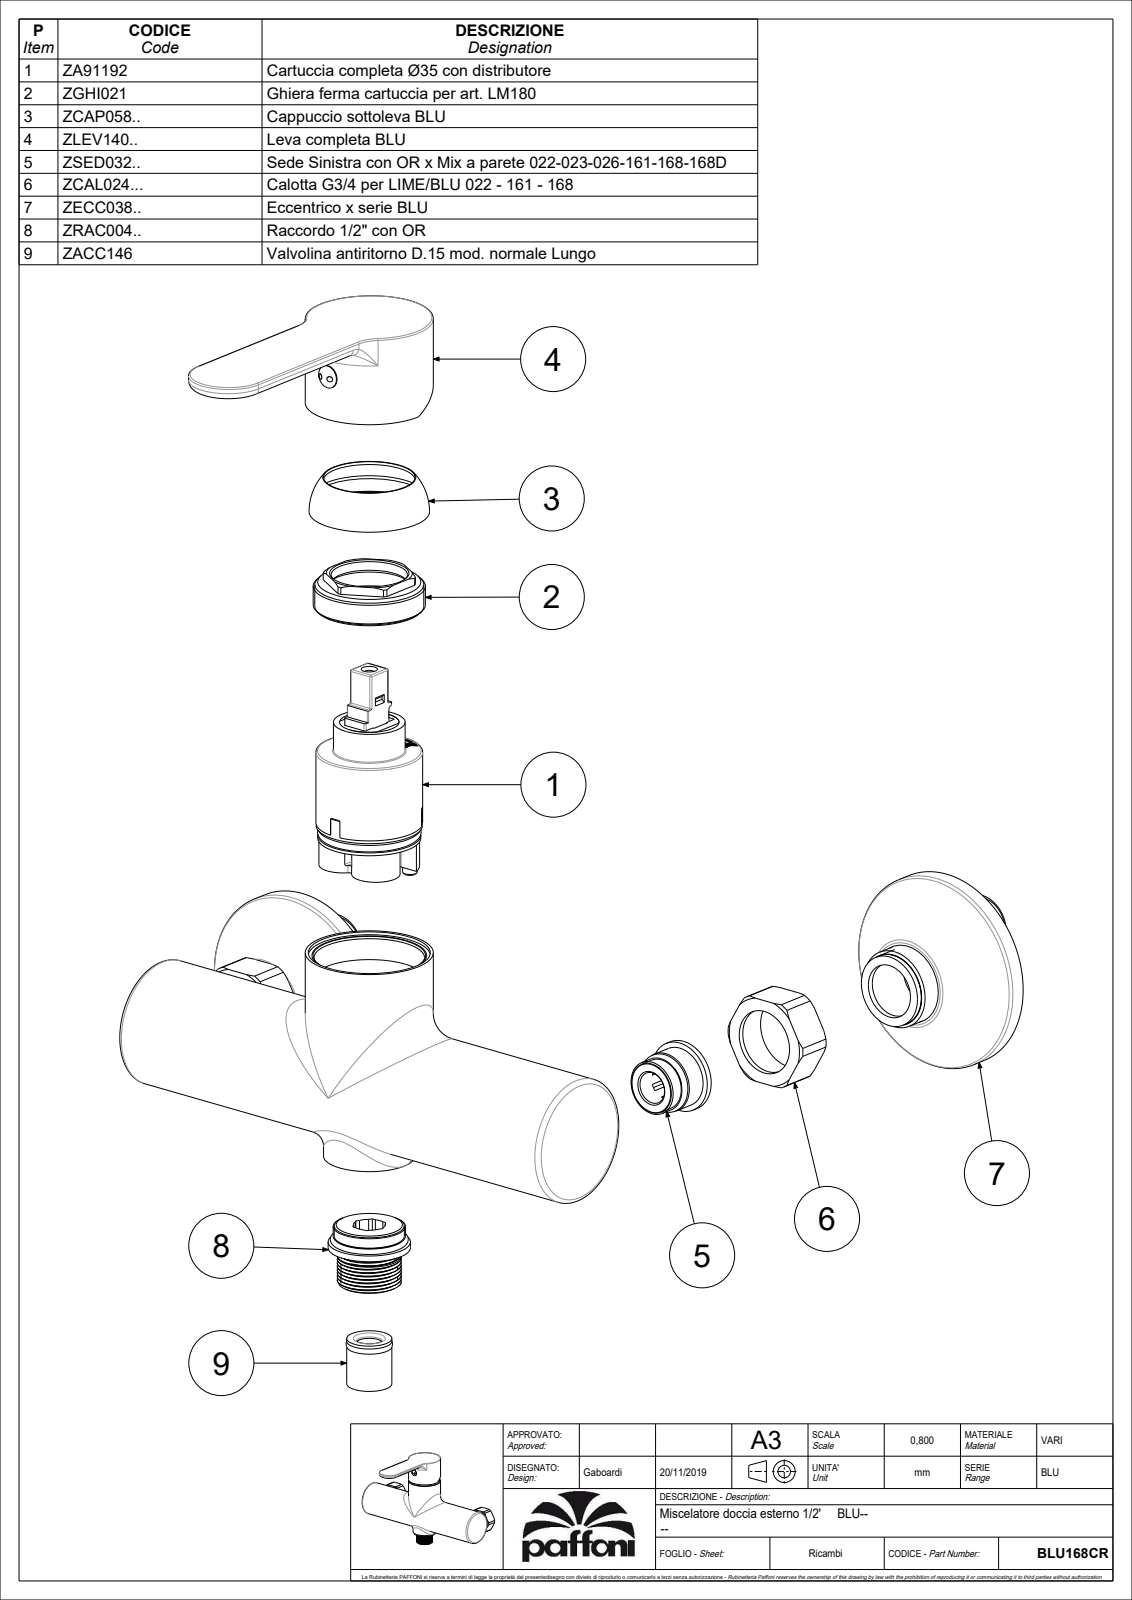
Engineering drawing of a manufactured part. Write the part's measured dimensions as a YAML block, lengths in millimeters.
part_name: "BLU168CR"
step_written_by: "CREO PARAMETRIC BY PTC INC, 2020044 (CONFIG_CONTROL_DESIGN)"
units: millimeters
bodies: {solids: 5, faces: 1177, planar: 482, cylindrical: 409, other: 286}
overall_size: [215.5, 142.2, 117.5]
volume: 141456
surface_area: 132259
round_holes:
  - {diameter: 12, count: 5}
  - {diameter: 9, count: 3}
  - {diameter: 3.3, count: 2}
  - {diameter: 7, count: 2}
  - {diameter: 8, count: 2}
  - {diameter: 16.3, count: 2}
  - {diameter: 17, count: 2}
  - {diameter: 18, count: 2}
  - {diameter: 21.5, count: 2}
  - {diameter: 24.1, count: 2}
  - {diameter: 38, count: 2}
  - {diameter: 63.5, count: 2}
round_bosses_or_shafts:
  - {diameter: 65.5, count: 2}
  - {diameter: 42, count: 2}
  - {diameter: 28.32, count: 2}
  - {diameter: 25, count: 2}
  - {diameter: 24, count: 2}
  - {diameter: 23.8, count: 2}
  - {diameter: 20.8, count: 2}
  - {diameter: 9, count: 2}
partial_cylinders:
  - {radius: 0.5, count: 64}
  - {radius: 0.3, count: 20}
  - {radius: 1, count: 13}
  - {radius: 1.2, count: 9}
  - {radius: 5.25, count: 3}
  - {radius: 7.25, count: 3}
  - {radius: 0.2, count: 2}
  - {radius: 1.6, count: 2}
face_to_face_distances: [2, 109, 69, 178, 1, 111, 67, 5.5, 20, 71]
hole_center_spacings: [0.71, 8.51, 8.6, 13.04, 13.21, 13.51, 97.31, 6]
